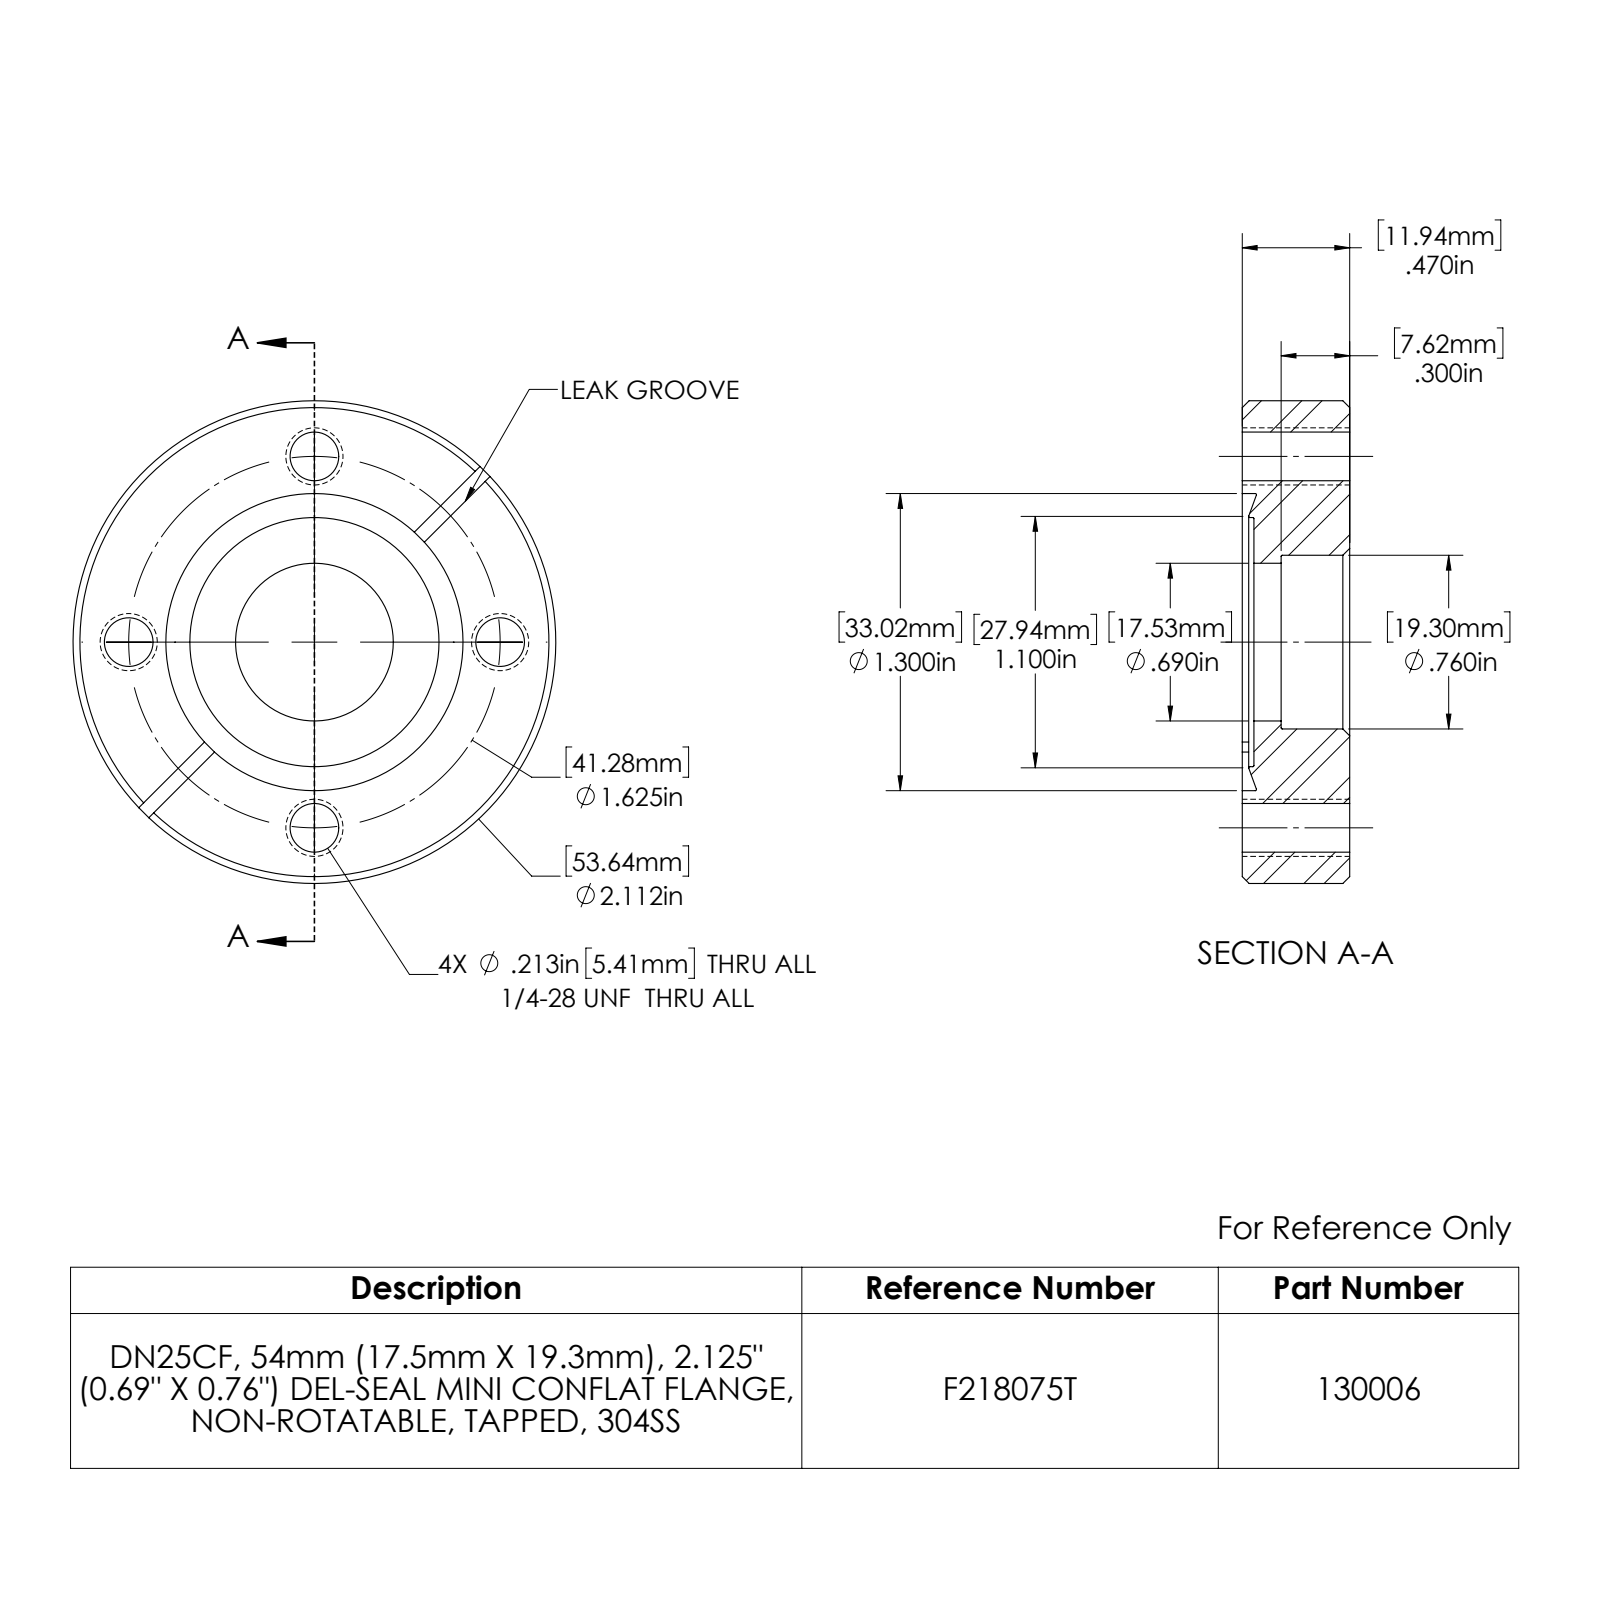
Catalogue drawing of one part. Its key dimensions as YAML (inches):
part_name: "130006_D"
step_written_by: "SolidWorks 2022 (CONFIG_CONTROL_DESIGN)"
units: inches
bodies: {solids: 1, faces: 46, planar: 9, cylindrical: 20, other: 17}
overall_size: [2.112, 2.112, 0.47]
volume: 1.321
surface_area: 11.53
round_holes:
  - {diameter: 0.213, count: 4}
  - {diameter: 0.69, count: 1}
  - {diameter: 0.76, count: 1}
  - {diameter: 1.09, count: 1}
  - {diameter: 1.3, count: 1}
round_bosses_or_shafts:
  - {diameter: 2.112, count: 1}
partial_cylinders:
  - {radius: 1.25, count: 2}
face_to_face_distances: [0.47, 0.051, 0.419, 0.062, 0.17, 0.119, 0.3]
hole_center_spacings: [0.813, 1.149, 1.625]
